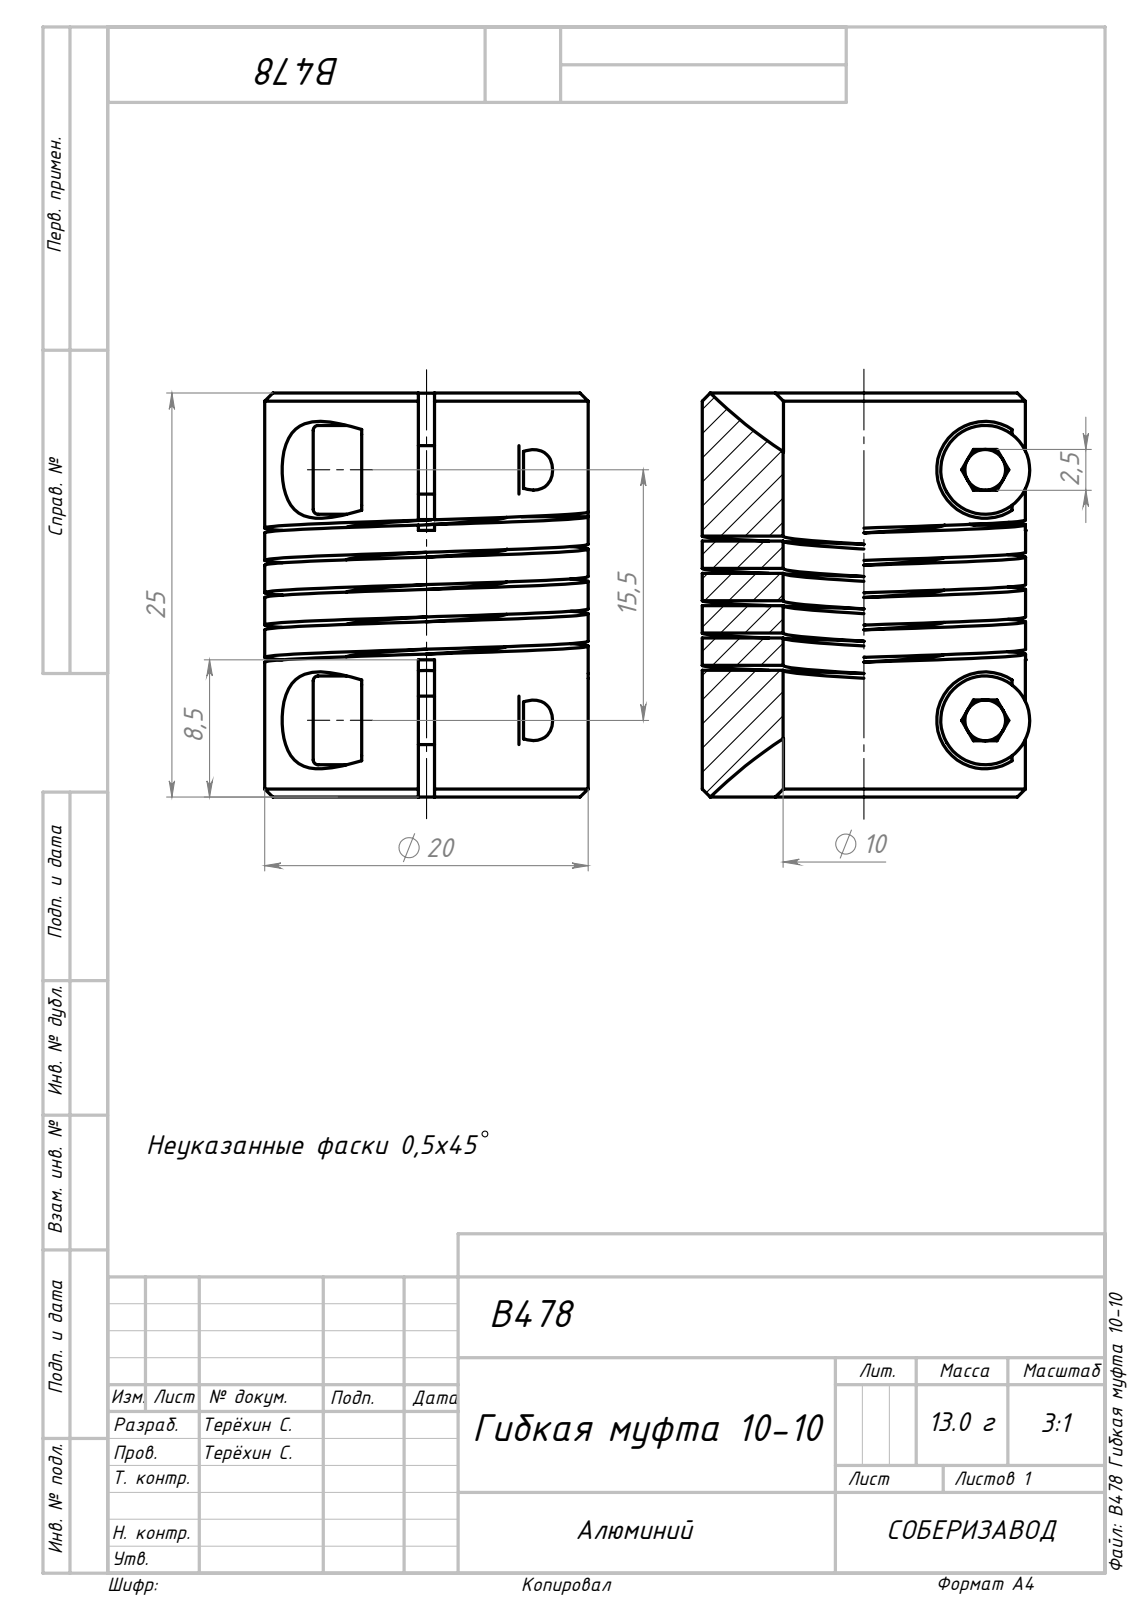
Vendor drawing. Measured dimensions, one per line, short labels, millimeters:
name: B478 Гибкая муфта 10-10; B478 Гибкая муфта 10-10_00; socket head cap screw_din_DIN 912 M3 x 10 --- 10N
written by: SolidWorks 2022 (AUTOMOTIVE_DESIGN)
unit: mm
bodies: 3 solids, 132 faces (48 planar, 53 cylindrical, 31 other)
size: 25 × 20.25 × 20
volume: 5 453 mm³; area: 5 715 mm²
holes: 2× ⌀2.5, 1× ⌀10
bosses: 2× ⌀5.5, 2× ⌀3, 1× ⌀20
rounds: 2× R3, 2× R30
face distances: 25, 1, 4.5, 3.5, 6.5, 7.5, 3, 2.52, 5.5, 10
hole spacings: 15.5
